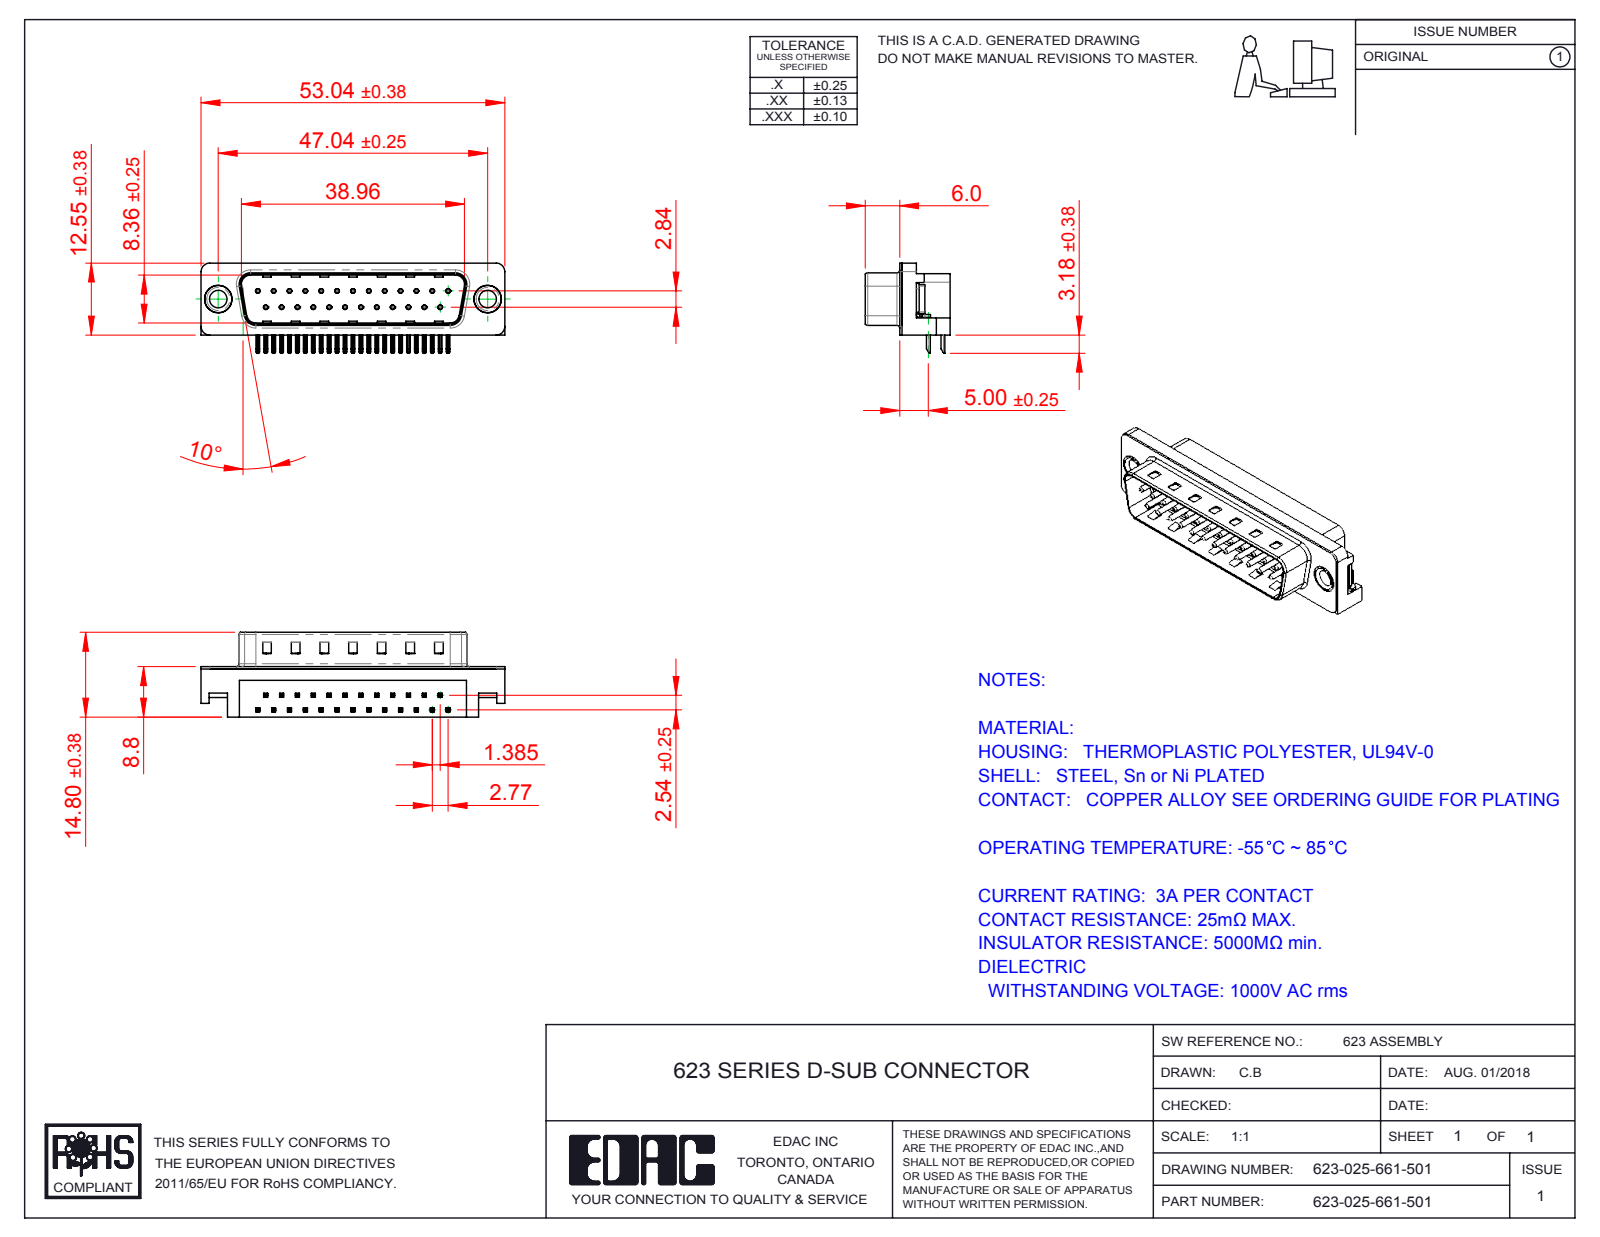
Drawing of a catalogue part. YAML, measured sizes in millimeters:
part_name: "623 Thru Hole Rivet; 623 Housing_25 Socket; 623 Non Board Mount; 623 Contact Bottom (+3 more)"
step_written_by: "SolidWorks 2016 (CONFIG_CONTROL_DESIGN)"
units: millimeters
bodies: {solids: 31, faces: 2213, planar: 1405, cylindrical: 631, other: 177}
overall_size: [53.04, 15.73, 14.8]
volume: 4712
surface_area: 6693
round_holes:
  - {diameter: 0.35, count: 25}
  - {diameter: 0.8, count: 25}
  - {diameter: 3.05, count: 2}
  - {diameter: 4, count: 2}
  - {diameter: 4.8, count: 2}
  - {diameter: 5, count: 2}
round_bosses_or_shafts:
  - {diameter: 0.75, count: 25}
  - {diameter: 4.9, count: 2}
  - {diameter: 4.75, count: 2}
  - {diameter: 3.85, count: 2}
partial_cylinders:
  - {radius: 0.25, count: 108}
  - {radius: 0.12, count: 50}
  - {radius: 1, count: 16}
  - {radius: 0.5, count: 9}
  - {radius: 1.5, count: 7}
  - {radius: 0.9, count: 4}
  - {radius: 1.6, count: 4}
  - {radius: 2, count: 4}
face_to_face_distances: [0.4, 8.4, 2.1, 1.7, 8.76, 10.46, 10.86, 10.35, 8.8, 5.9]
hole_center_spacings: [3.16, 2.77, 11.08, 5.54, 8.31, 5.03, 13.85, 7.48]
